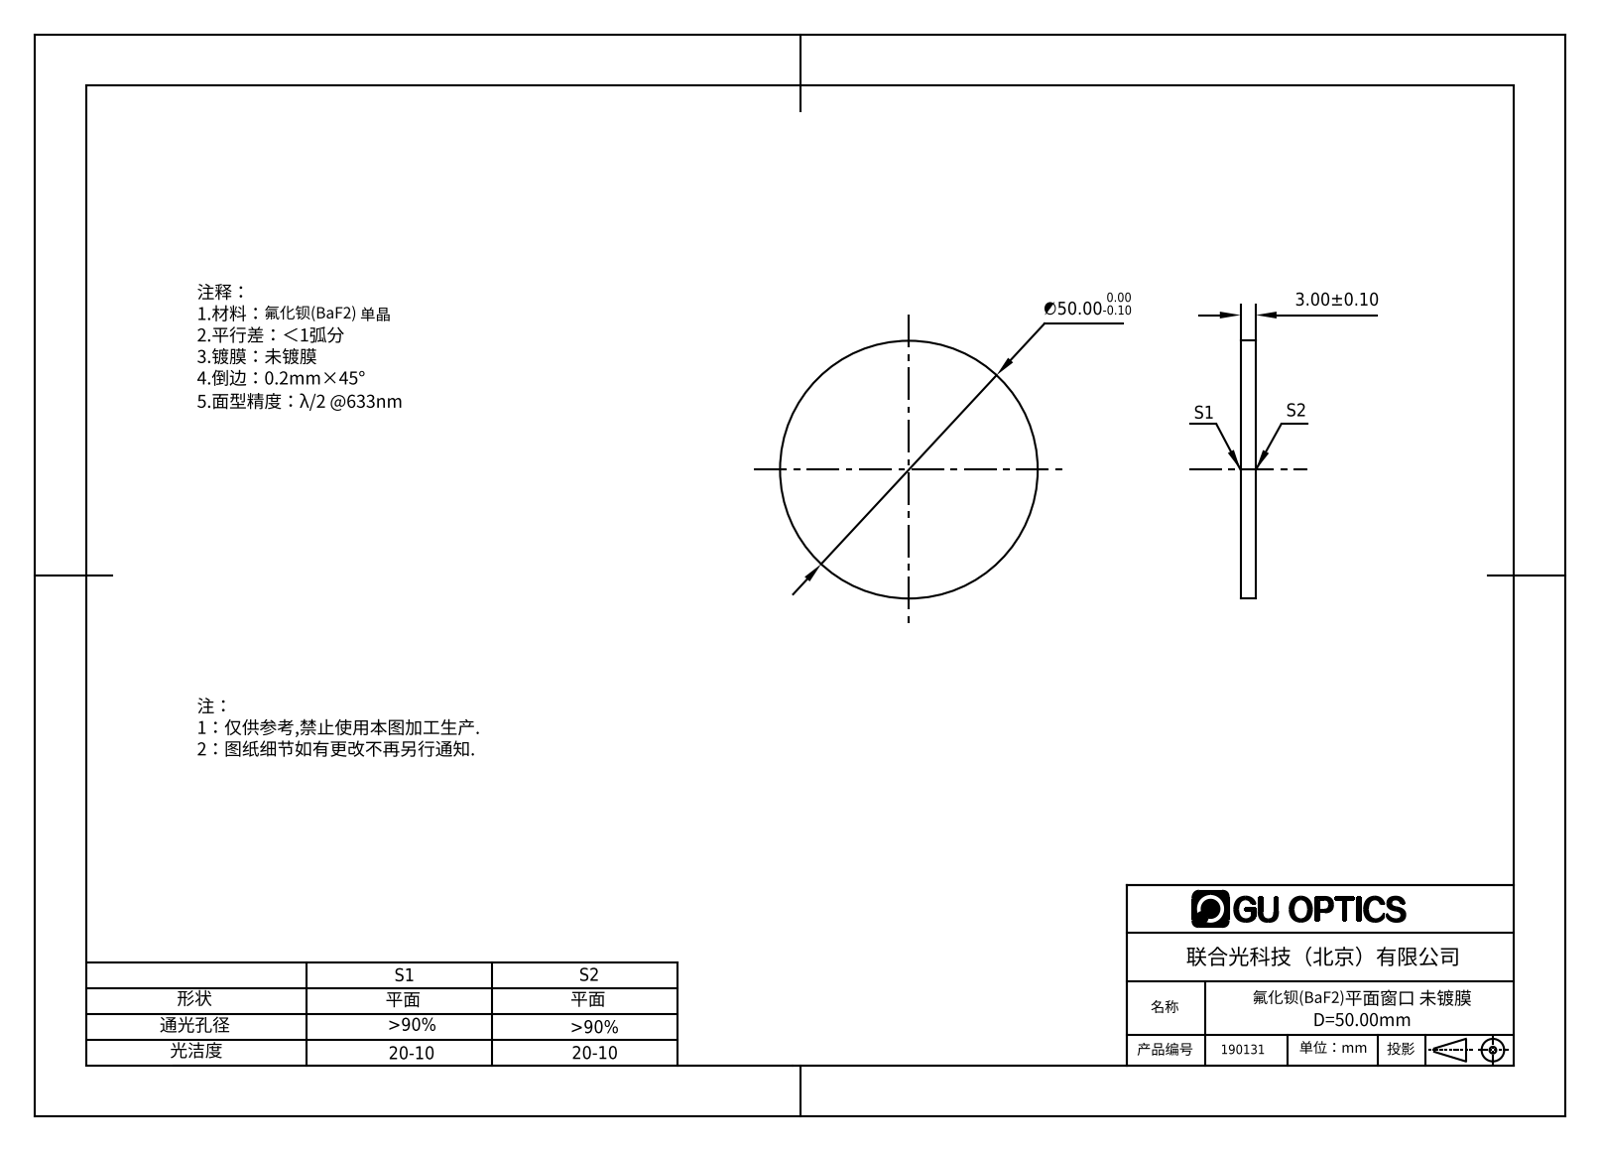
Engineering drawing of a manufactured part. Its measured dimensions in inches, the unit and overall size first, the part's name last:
Units: inches
Overall size (bounding box): 1.969 × 1.969 × 0.118
Round bosses / shafts (diameter × count): ⌀1.969 ×1
Main face-to-face distances: 0.118
Volume: 0.359 in³ · Surface area: 6.817 in²
Bodies: 1 solid, 4 faces (2 planar, 2 cylindrical, 0 other)
Part name (STEP PRODUCT): 190131
STEP written by: SolidWorks 2016 (AUTOMOTIVE_DESIGN)
